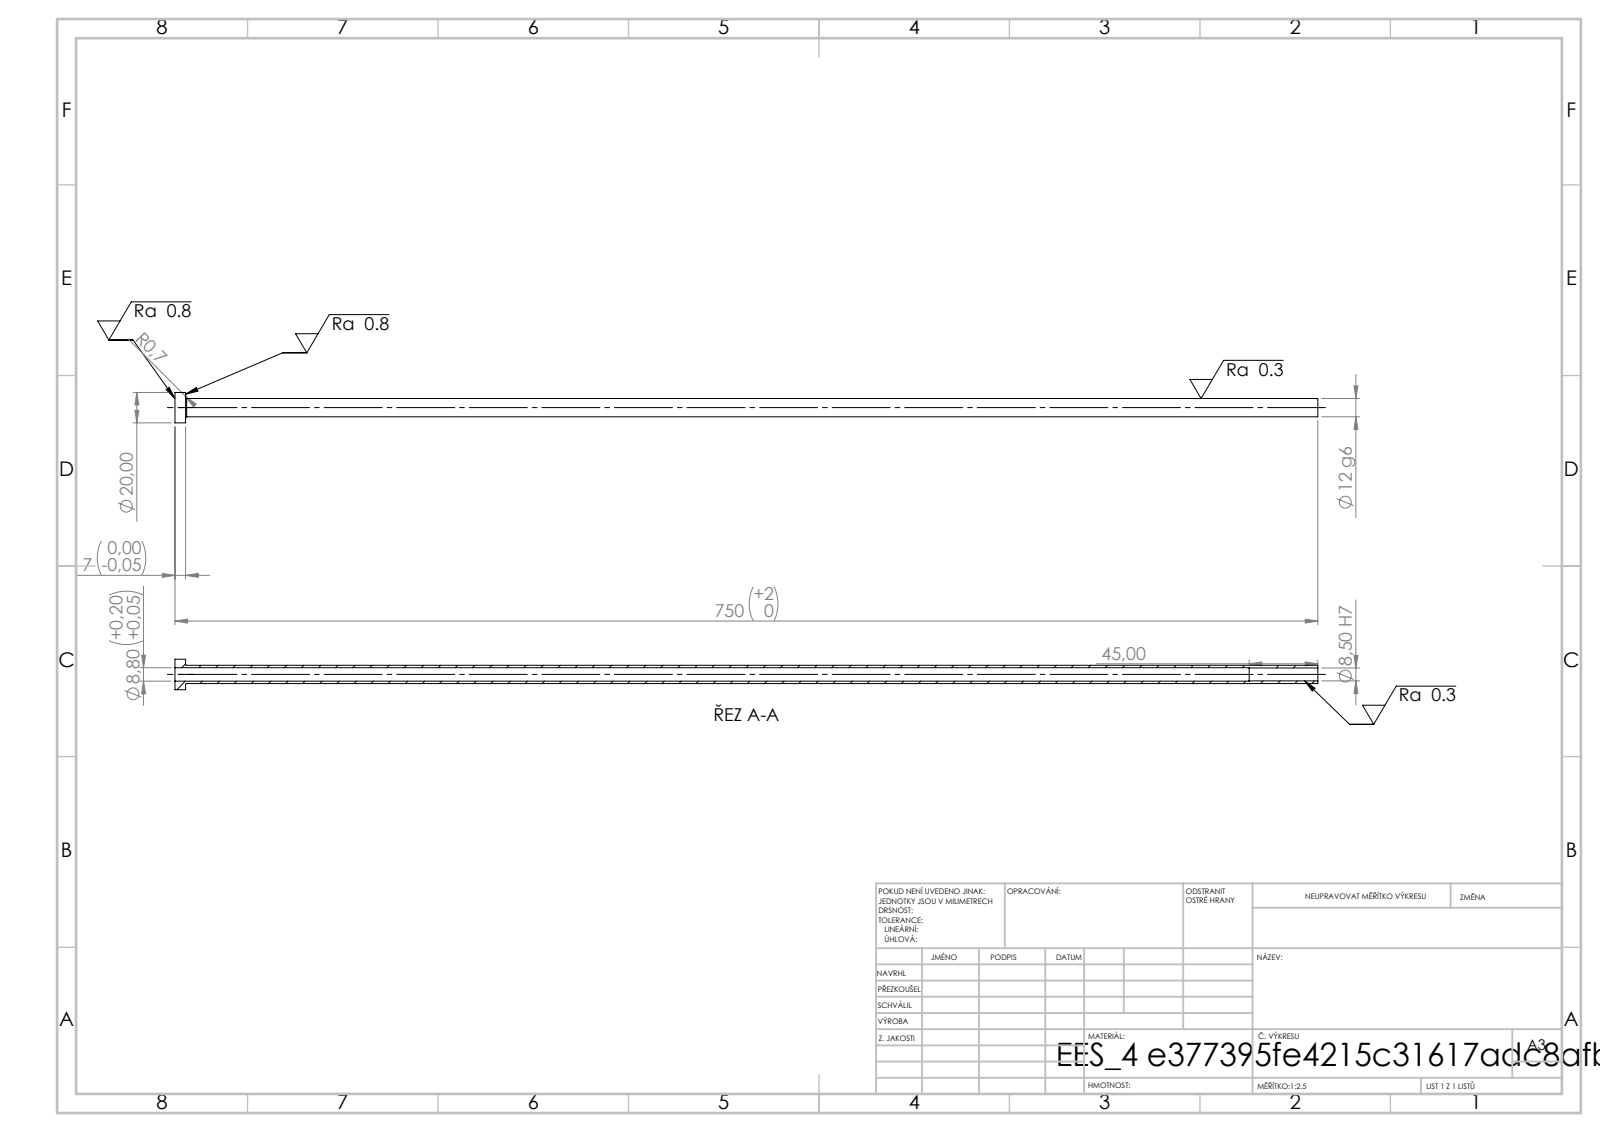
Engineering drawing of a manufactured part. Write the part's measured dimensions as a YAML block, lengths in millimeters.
step_written_by: "SolidWorks 2019 (CONFIG_CONTROL_DESIGN)"
units: millimeters
bodies: {solids: 1, faces: 14, planar: 4, cylindrical: 8, other: 2}
overall_size: [750, 20, 20]
volume: 40802
surface_area: 49646
round_holes:
  - {diameter: 8.5, count: 1}
  - {diameter: 8.8, count: 1}
round_bosses_or_shafts:
  - {diameter: 20, count: 1}
  - {diameter: 12, count: 1}
face_to_face_distances: [7, 750, 743, 705, 698, 45]
